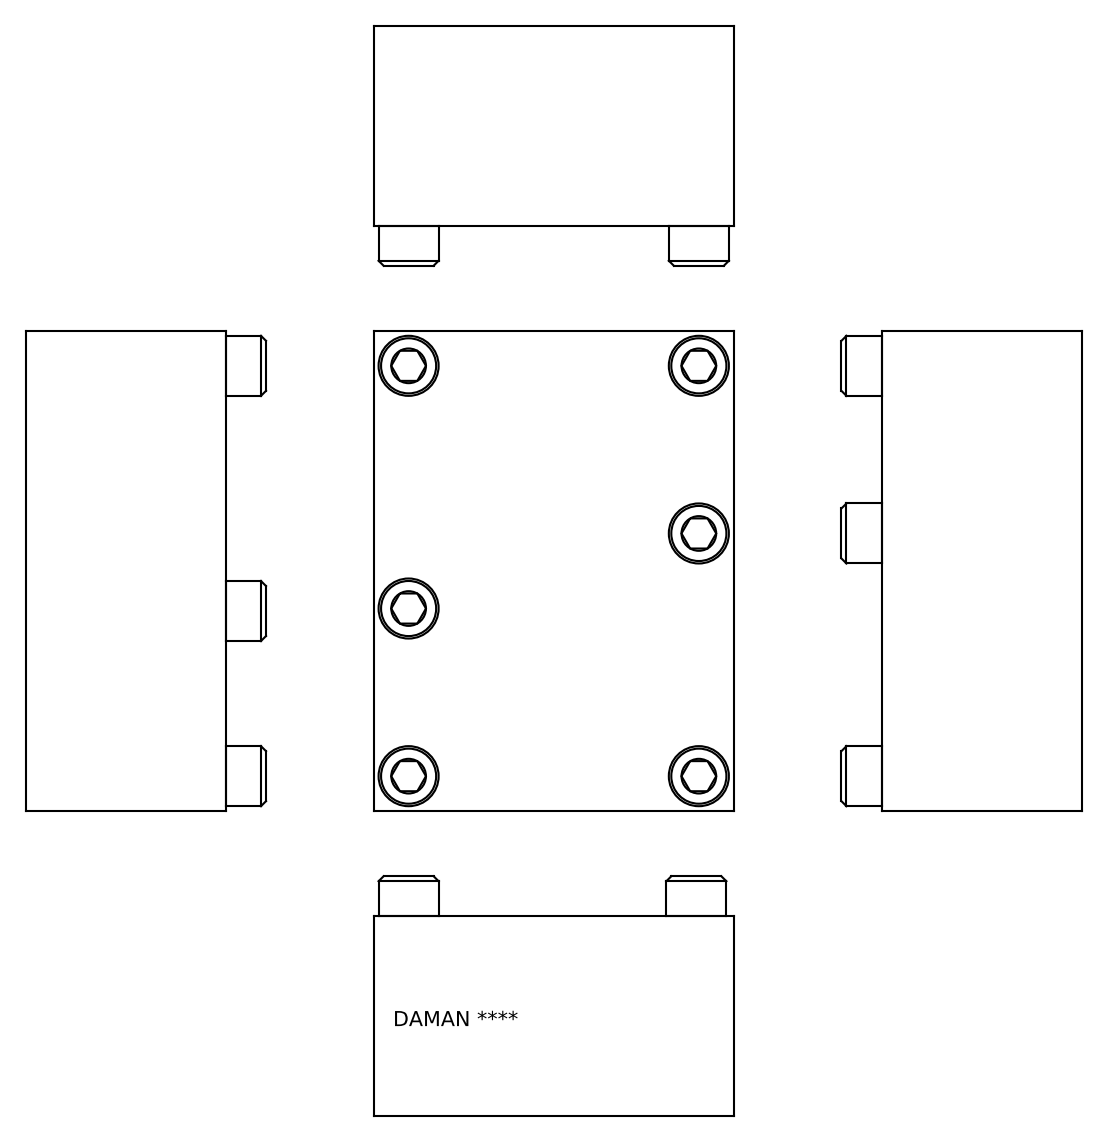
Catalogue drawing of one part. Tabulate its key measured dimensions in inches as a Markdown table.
| quantity | value |
| --- | --- |
| part name | Part_AD08COP_3D |
| STEP written by | Autodesk Inventor 2020 (AUTOMOTIVE_DESIGN) |
| units | inches |
| bodies | 1 solid, 309 faces (202 planar, 18 cylindrical, 89 other) |
| overall size | 6 × 4.5 × 2.5 |
| volume | 61.76 in³ |
| surface area | 136.1 in² |
| round holes (diameter × count) | 0.531 × 6, 0.25 × 2, 0.906 × 2, 1 × 2, 1.313 × 2 |
| partial cylindrical surfaces (radius × count) | 0.453 × 2, 0.657 × 2 |
| main face-to-face distances | 2.5, 4.5, 6, 0.11, 2.39, 0.39, 0.5, 2, 0.906, 1.11 |
| hole center spacings | 1.345, 3.157, 4.028, 4.938, 5.125, 6.278, 0.886, 1.017 |
